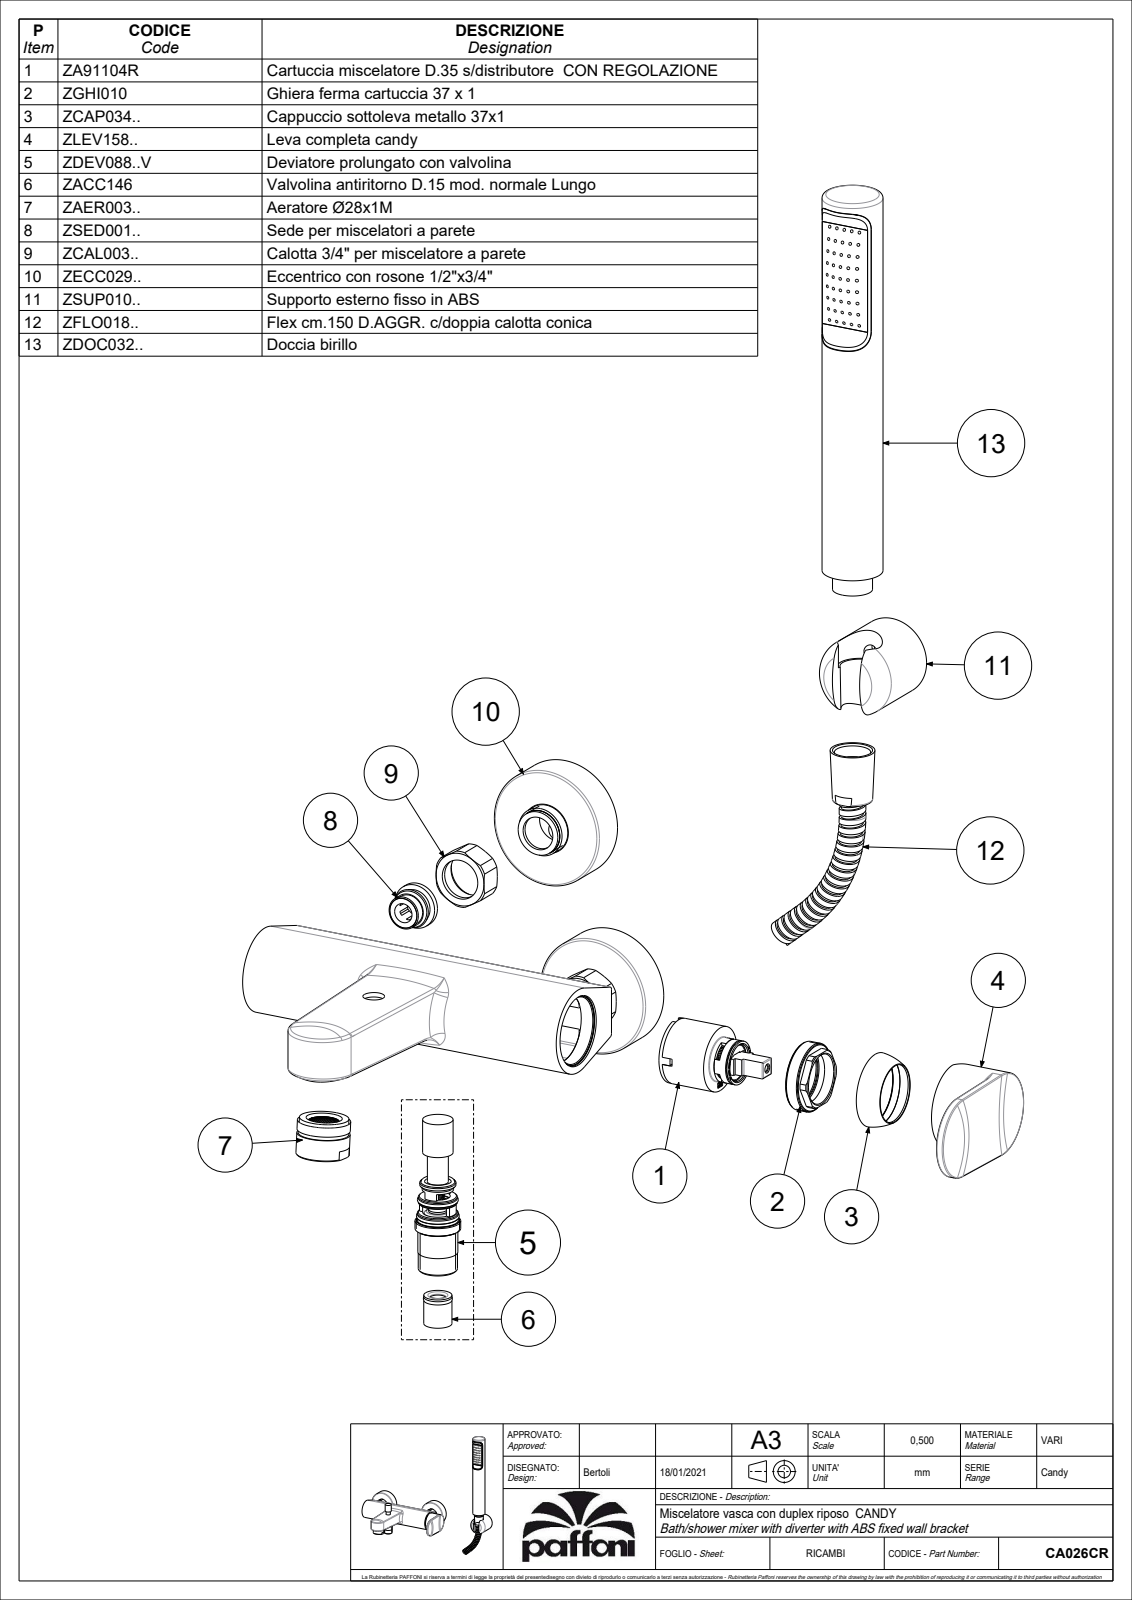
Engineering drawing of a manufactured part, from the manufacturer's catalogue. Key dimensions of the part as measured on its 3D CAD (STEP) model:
Part name (STEP PRODUCT): CA026CR
STEP written by: CREO PARAMETRIC BY PTC INC, 2020044 (CONFIG_CONTROL_DESIGN)
Units: millimetres
Bodies: 6 solids, 2313 faces (1644 planar, 280 cylindrical, 389 other)
Overall size (bounding box): 352.75 × 331.8 × 191.5
Volume: 619 781 mm³ · Surface area: 200 579 mm²
Round holes (diameter × count): ⌀5 ×2, ⌀16.5 ×2, ⌀19 ×2, ⌀22 ×2, ⌀28.5 ×2, ⌀3 ×1, ⌀3.5 ×1, ⌀4.5 ×1, ⌀8 ×1, ⌀10 ×1, ⌀11 ×1, ⌀12.8 ×1
Round bosses / shafts (diameter × count): ⌀63.5 ×2, ⌀21 ×2, ⌀45 ×1, ⌀42 ×1, ⌀32 ×1, ⌀28 ×1, ⌀26.5 ×1, ⌀22 ×1
Partial cylindrical surfaces — rounded edges, fillets, slot ends (radius × count): R1 ×91, R3 ×4, R1.5 ×2, R15.5 ×2, R3.5 ×1, R9 ×1, R9.75 ×1, R11.75 ×1
Main face-to-face distances: 3.5, 20, 14.5, 34.5, 3, 5, 18, 0.5, 38, 17
Hole centre spacings: 6, 39.6, 110.77, 150, 150.27, 189.6, 300.13
